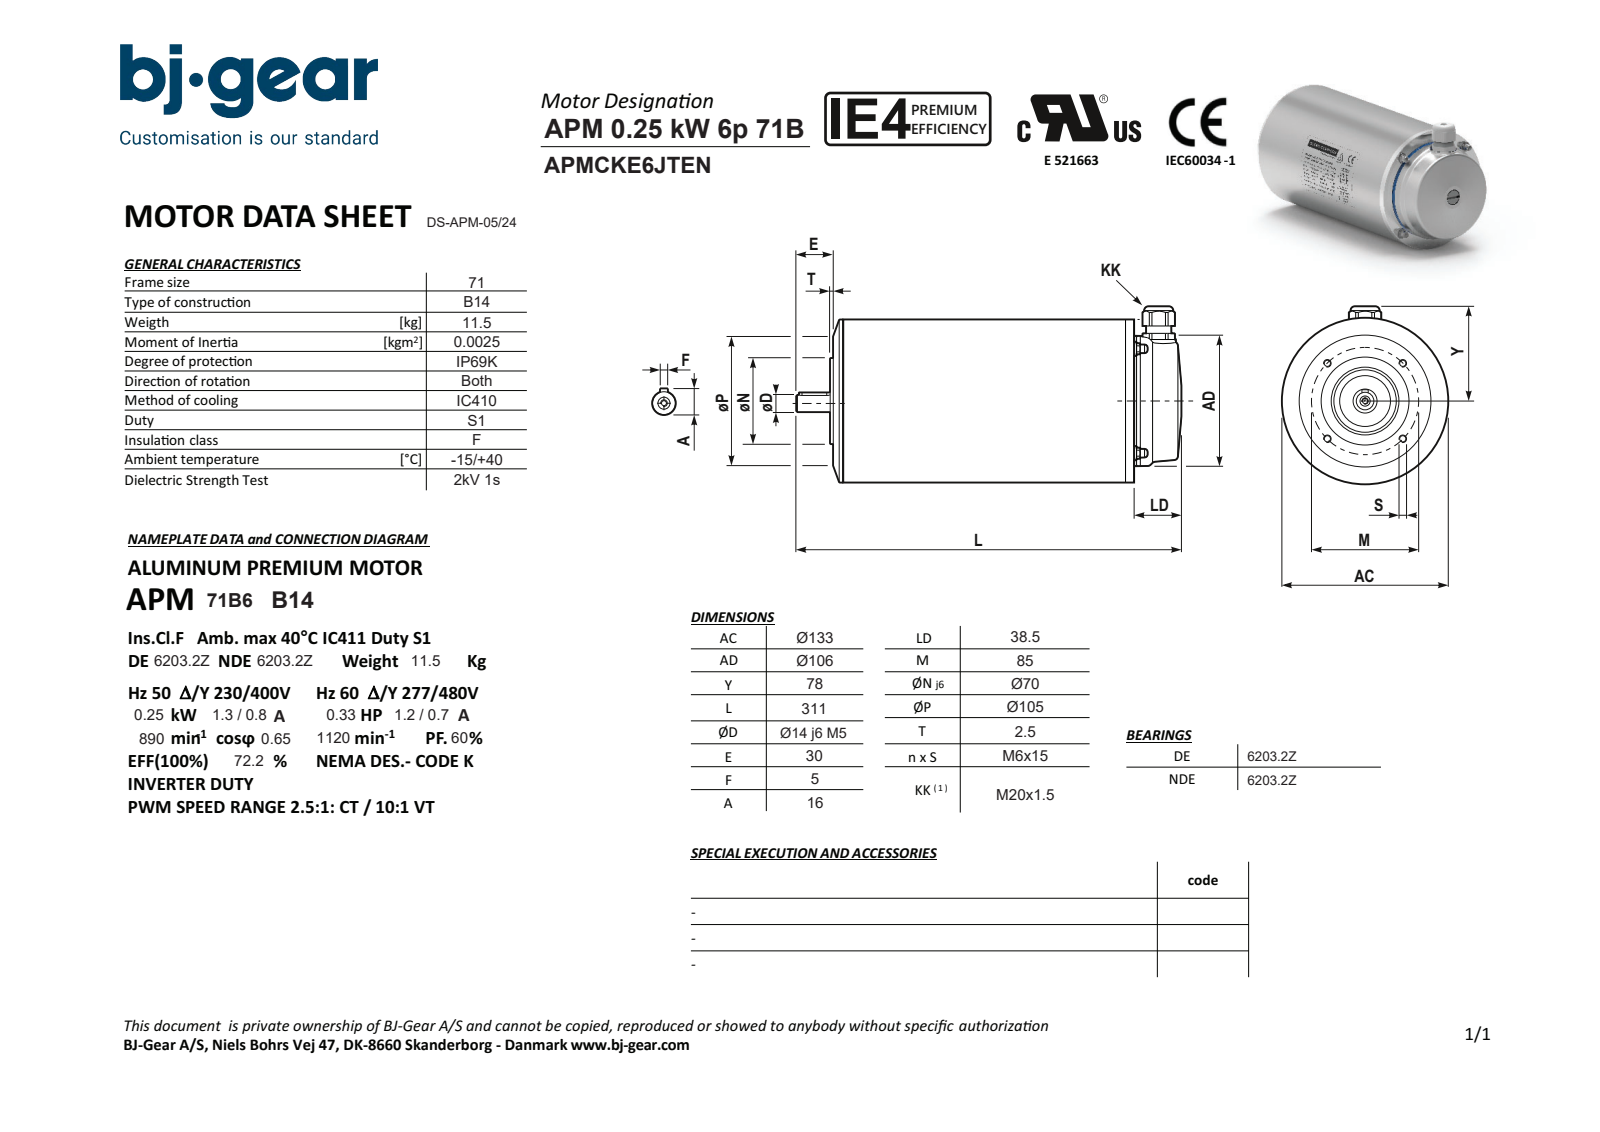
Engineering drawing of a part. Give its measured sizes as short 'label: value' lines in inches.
name: APMCKE6JTENN4KCR2-N---NNN
written by: Solid Edge (AUTOMOTIVE_DESIGN)
unit: in
bodies: 1 solid, 156 faces (71 planar, 50 cylindrical, 35 other)
size: 12.244 × 5.642 × 5.22
volume: 222.1 in³; area: 225 in²
holes: 4× ⌀0.194, 1× ⌀0.163, 1× ⌀0.209, 1× ⌀0.63, 1× ⌀1.102, 1× ⌀2.047
bosses: 4× ⌀0.453, 4× ⌀0.276, 1× ⌀5.22, 1× ⌀5.22, 1× ⌀4.173, 1× ⌀2.756, 1× ⌀0.933, 1× ⌀0.811
rounds: 2× R0.098, 1× R0.52
face distances: 9.547, 9.331, 0.217, 0.315, 0.098, 9.646, 11.161, 1.516, 10.846, 11.063
hole spacings: 1.673, 2.366, 3.346
